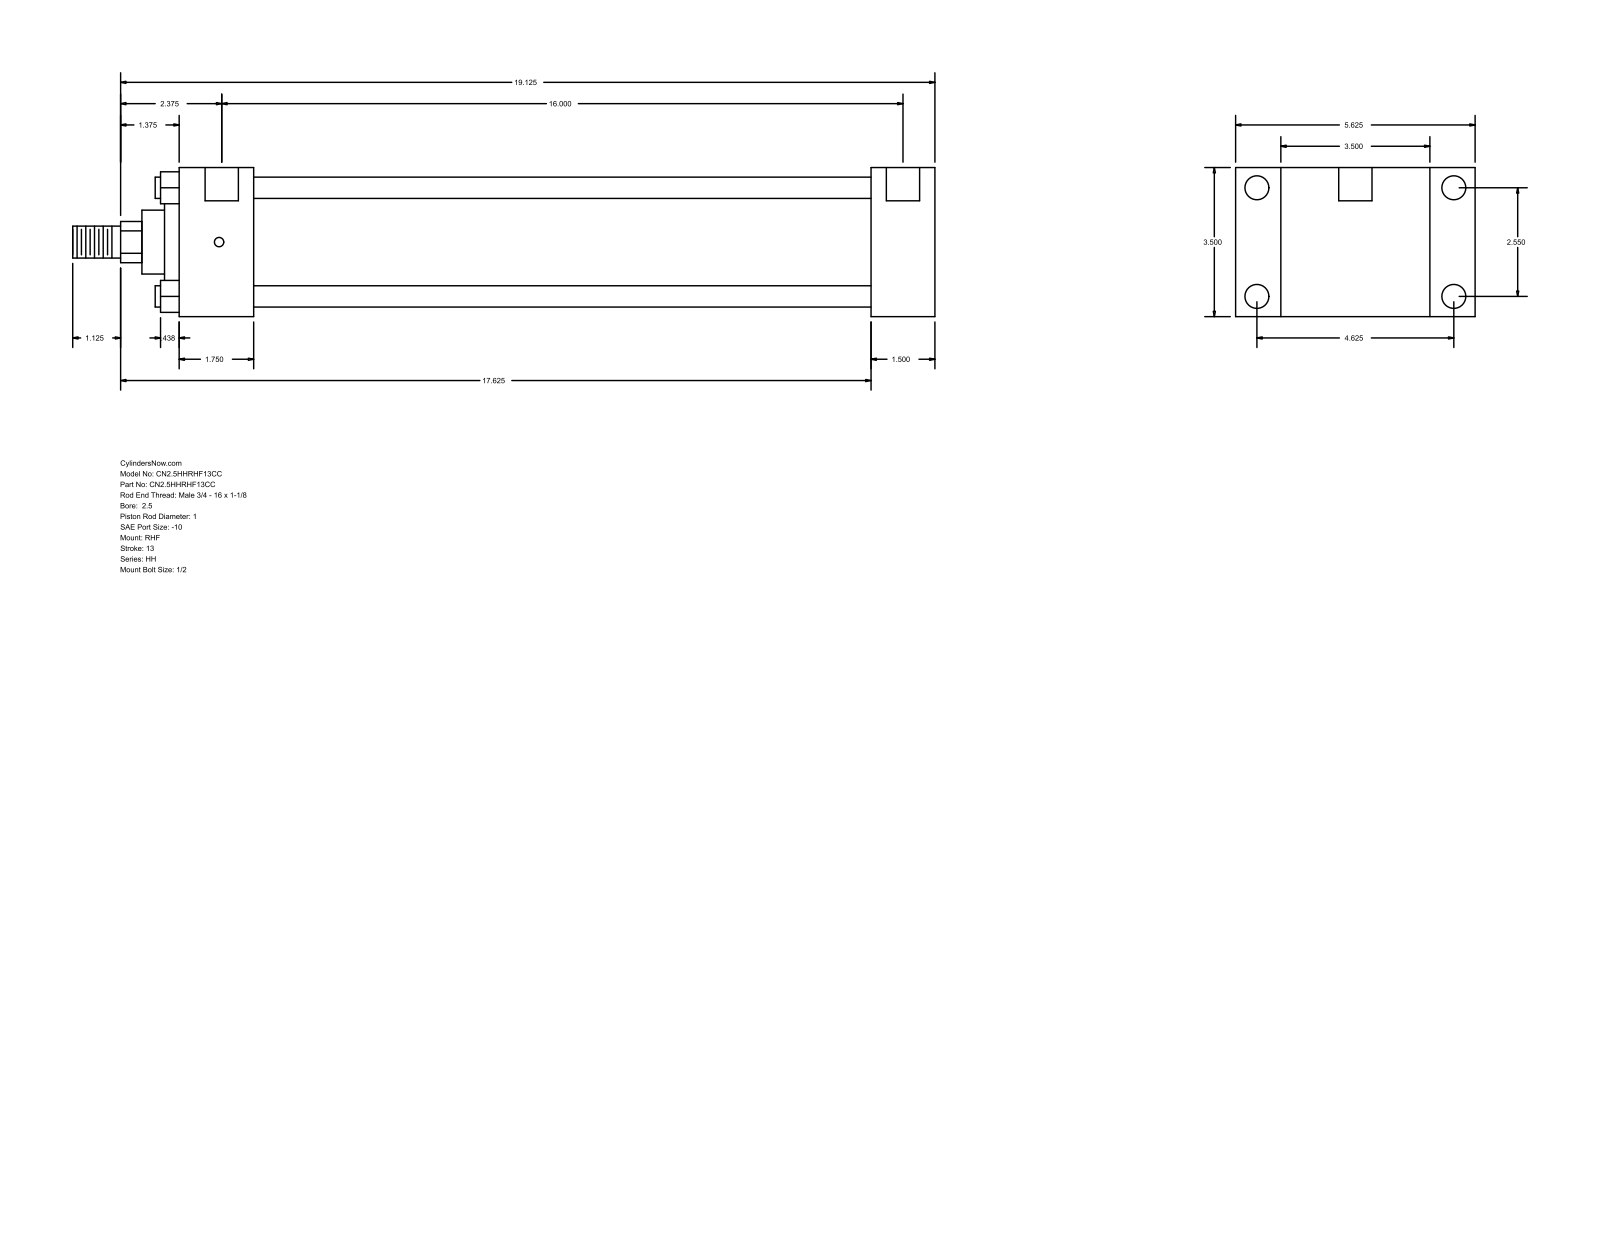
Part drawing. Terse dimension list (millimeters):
name: HH_RHF__0250_1
written by: GSSL Pune (CONFIG_CONTROL_DESIGN)
unit: mm
bodies: 0 solids, 90 faces (61 planar, 29 cylindrical, 0 other)
size: 514.35 × 142.88 × 88.9
holes: 4× ⌀5.56, 4× ⌀14.3, 2× ⌀19.84
bosses: 4× ⌀12.7, 1× ⌀73.03, 1× ⌀60.33, 1× ⌀38.1, 1× ⌀25.4, 1× ⌀19.05
rounds: 1× R12.29
face distances: 88.9, 38.09, 26.99, 115.89, 412.76, 450.85, 142.88, 44.46, 368.3, 406.39
hole spacings: 64.76, 117.48, 134.15, 409.57, 1.58, 1.59, 406.4, 407.98
